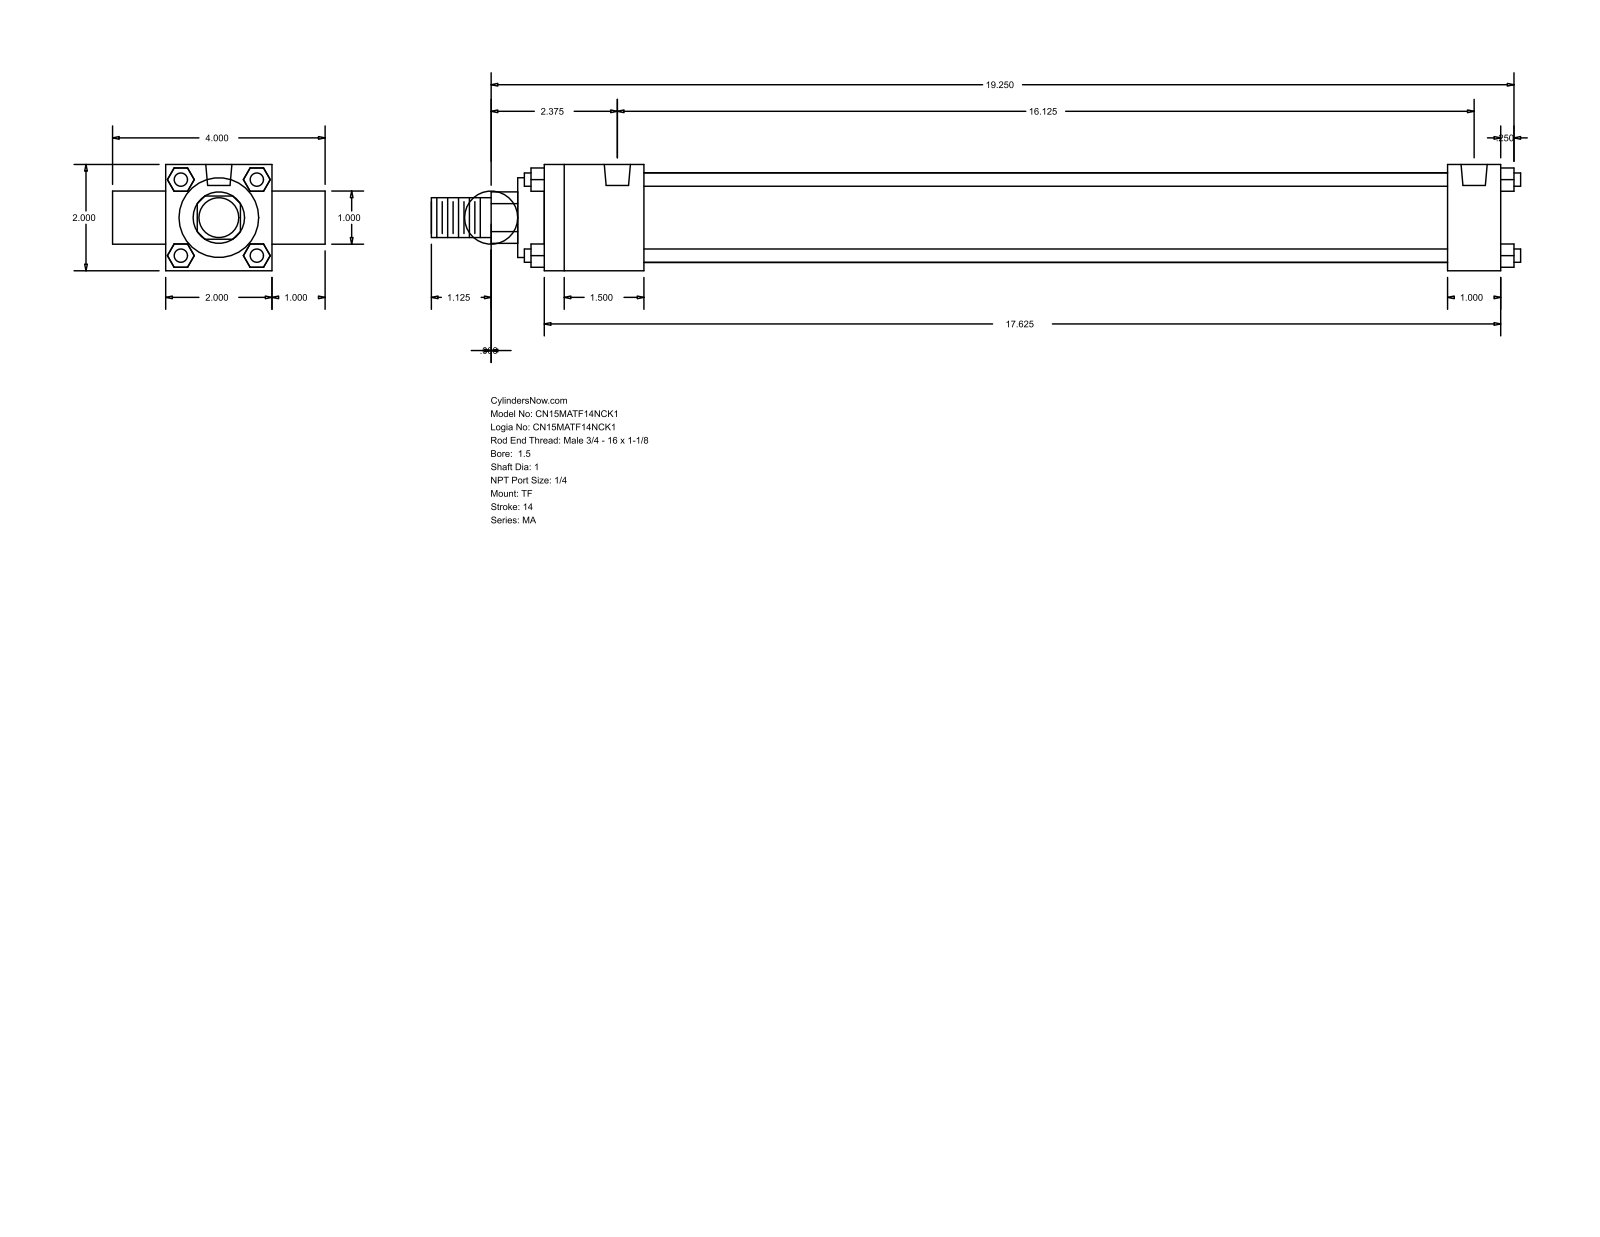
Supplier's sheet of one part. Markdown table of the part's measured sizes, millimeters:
| quantity | value |
| --- | --- |
| part name | MA_TF__0150_1 |
| STEP written by | GSSL Pune (CONFIG_CONTROL_DESIGN) |
| units | millimeters |
| bodies | 0 solids, 120 faces (92 planar, 28 cylindrical, 0 other) |
| overall size | 520.7 × 101.6 × 50.8 |
| round holes (diameter × count) | 7.94 × 3, 12.49 × 2 |
| round bosses / shafts (diameter × count) | 6.35 × 4, 25.4 × 2, 42.93 × 1, 38.1 × 1, 19.05 × 1 |
| partial cylindrical surfaces (radius × count) | 12.29 × 1 |
| main face-to-face distances | 50.8, 25.4, 457.2, 76.2, 6.35, 47.63, 431.8, 384.17, 409.57, 469.9 |
| hole center spacings | 409.57 |
